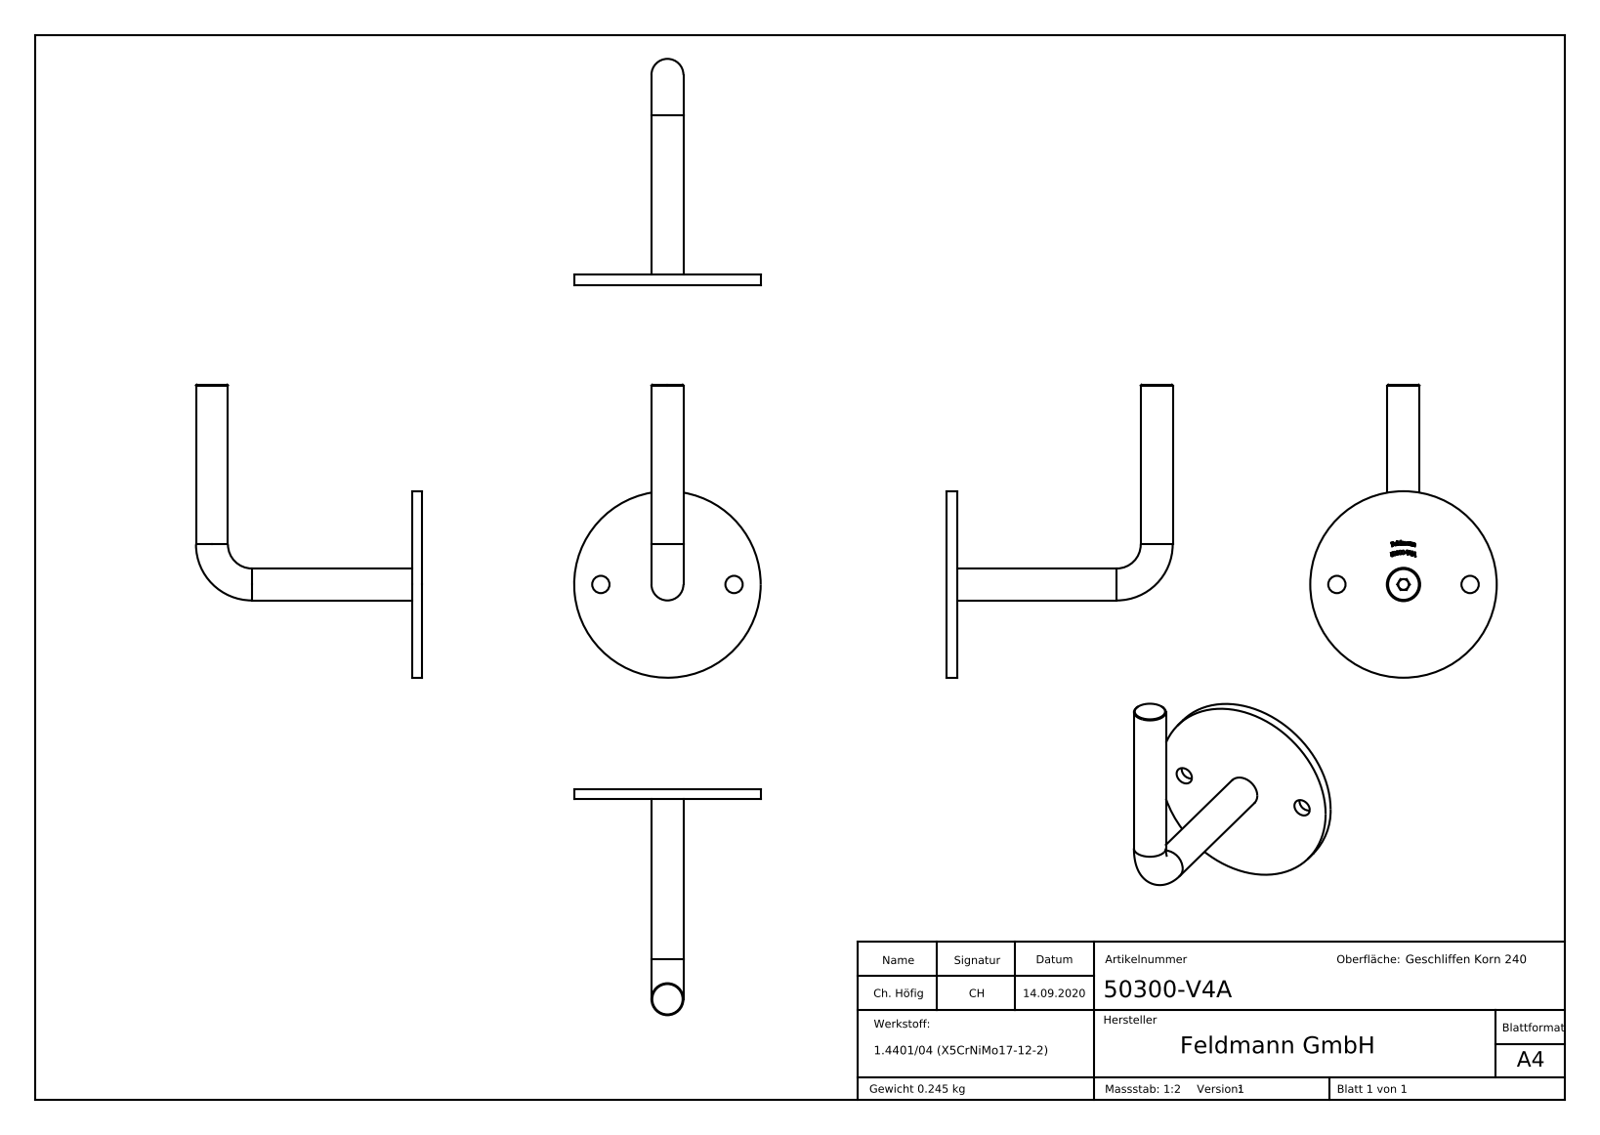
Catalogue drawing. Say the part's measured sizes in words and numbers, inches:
The part is named "50300-V4A Teil1_50300-V4A Teil1; 50300-V4A Teil1; 50300-V4A Teil2; socket countersunk head screw_din_DIN 7991 - M6 x 16 --- 9.7S (+3 more)". Its 3-D file was written by "SolidWorks 2018 (CONFIG_CONTROL_DESIGN)". It is 3 solids with 334 faces: 141 planar, 38 cylindrical and 155 other. Overall it measures 4.331 by 3.346 by 2.756 inches. Its volume is 1.899 cubic inches and its surface area 23.6 square inches. Round holes: 2 of diameter 0.256, 1 of diameter 0.197, 1 of diameter 0.492. Round bosses or shafts: 2 of diameter 0.472, 1 of diameter 2.756, 1 of diameter 0.456, 1 of diameter 0.236. The main face-to-face distances are 0.157, 0.037, 0.12, 0.667, 0.63, 0.51, 0.158, 0.02, 0.018, 0.138. The hole center spacings are 0.984, 1.969.
